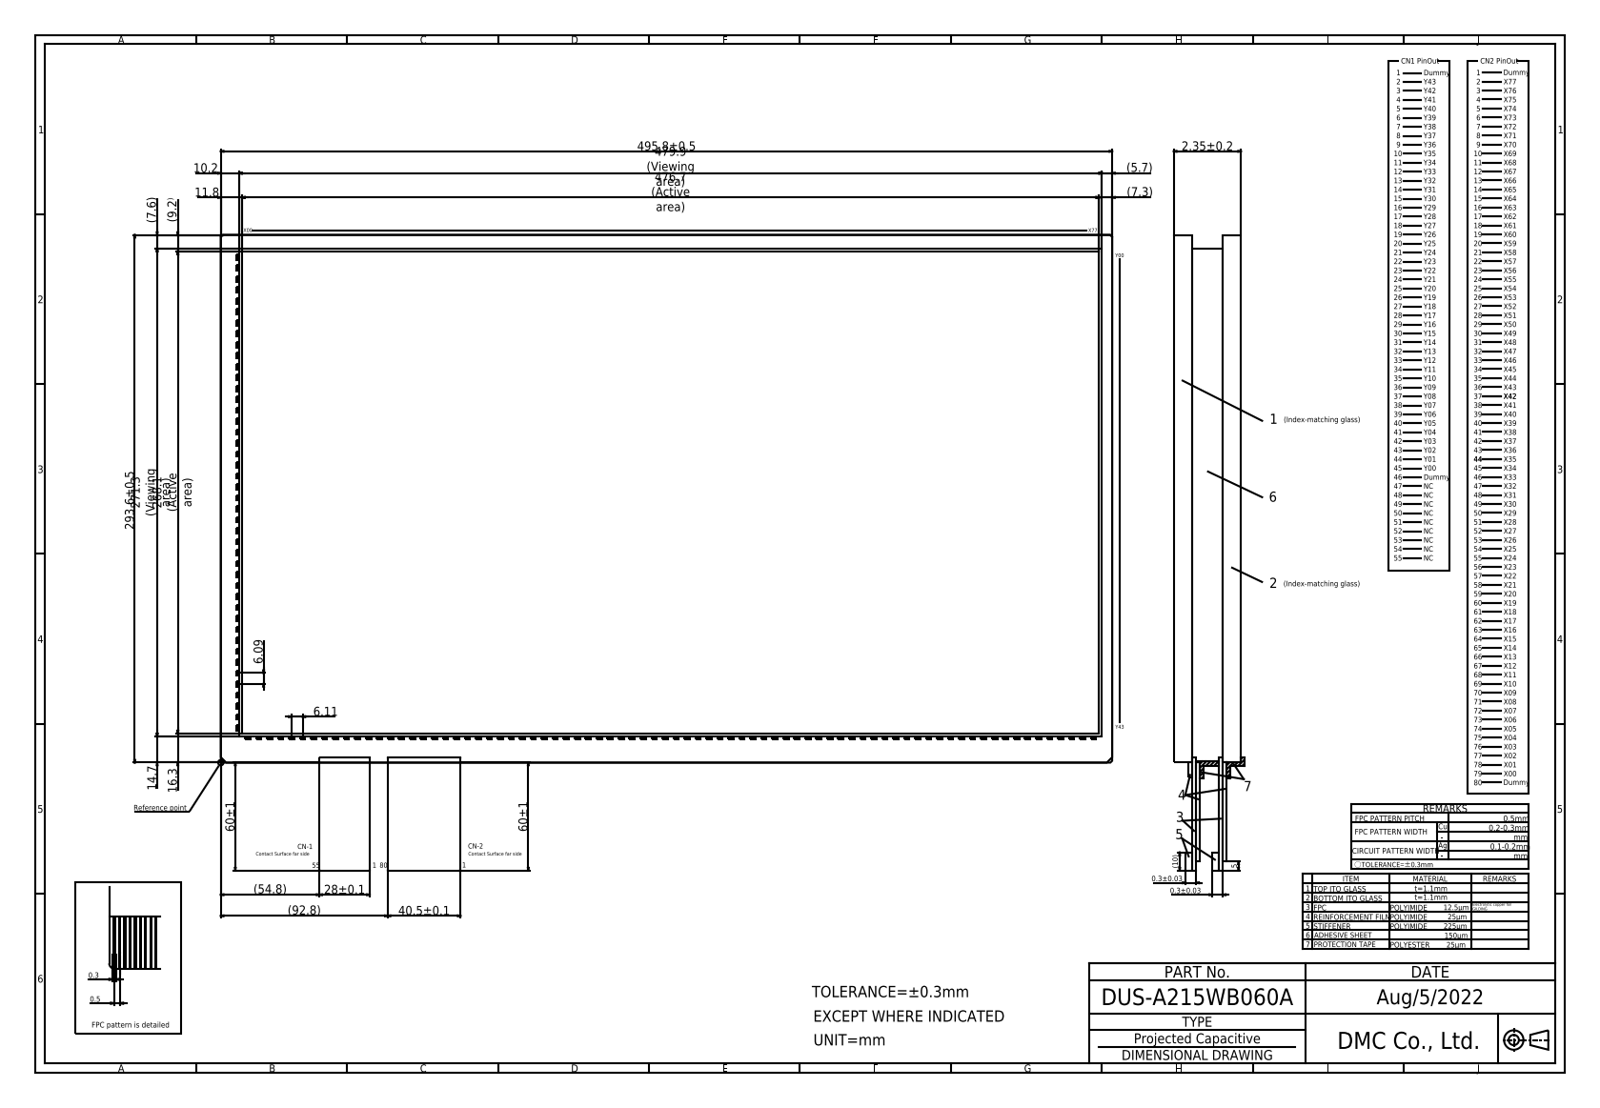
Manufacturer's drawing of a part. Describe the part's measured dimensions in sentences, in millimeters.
The part is named "DUS-A215WB060A". Its 3-D file was written by "Autodesk Inventor 2020 (CONFIG_CONTROL_DESIGN)". It is 1 solid with 578 faces: 574 planar, 4 cylindrical and 0 other. Overall it measures 694.12 by 412.32 by 2.35 millimeters. Its volume is 342 424 cubic millimeters and its surface area 303 451 square millimeters. Partial cylindrical surfaces (rounded edges, fillets, slot ends): 4 of radius 0.2. The main face-to-face distances are 2.35, 1.1, 1.2, 1.15, 1.25, 1, 2.25, 293.6, 495.8, 0.8.
